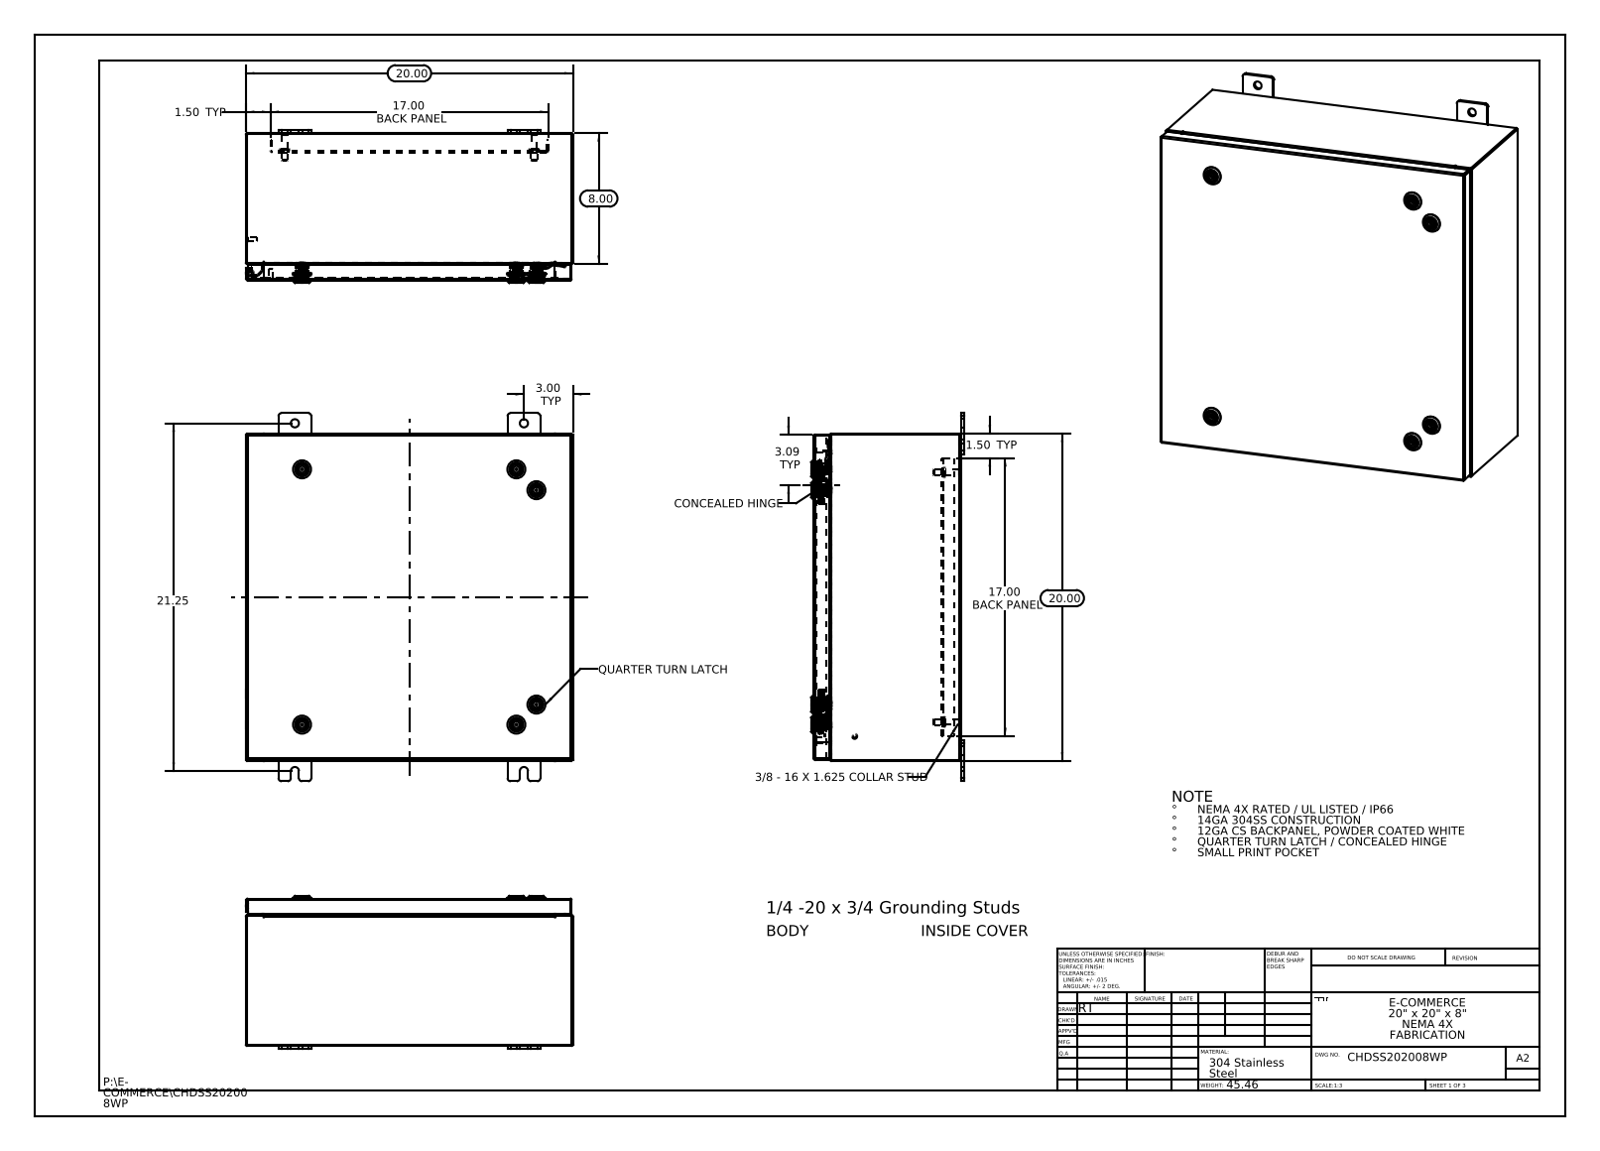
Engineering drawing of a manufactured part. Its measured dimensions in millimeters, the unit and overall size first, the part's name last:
Units: millimetres
Overall size (bounding box): 571.5 × 508 × 237.6
Round holes (diameter × count): ⌀12.7 ×8, ⌀5 ×6, ⌀10 ×6, ⌀10.2 ×6, ⌀16 ×6, ⌀20 ×6, ⌀3.5 ×4, ⌀5.4 ×2
Round bosses / shafts (diameter × count): ⌀6 ×8, ⌀28 ×6, ⌀19.8 ×6, ⌀15.9 ×6, ⌀15.5 ×6, ⌀13.5 ×6, ⌀10 ×6, ⌀2.9 ×6
Partial cylindrical surfaces — rounded edges, fillets, slot ends (radius × count): R0.2 ×198, R3 ×198, R0.7 ×72, R0.5 ×24, R4.8 ×24, R5 ×24, R0.3 ×20, R2.2 ×18
Main face-to-face distances: 1.9, 506.1, 1.9, 228.9, 226.9, 227, 225.1, 504.2, 508, 2.6
Hole centre spacings: 332.7, 47.2, 77.9, 355.6, 365.2, 387.4, 387.4, 396.2
Volume: 2 674 000 mm³ · Surface area: 2 637 000 mm²
Bodies: 55 solids, 5420 faces (1592 planar, 1692 cylindrical, 2136 other)
Part name (STEP PRODUCT): HW-CLH-R001-0500_2412-026240-2445-Industrilas; CHDSS202008WP Mounting Studs; Nut-211301-IB-Industrilas_Nut-211301-IB-Industrilas; CHDSS202008WP Bottom (+8 more)
STEP written by: SolidWorks 2013 (CONFIG_CONTROL_DESIGN)
